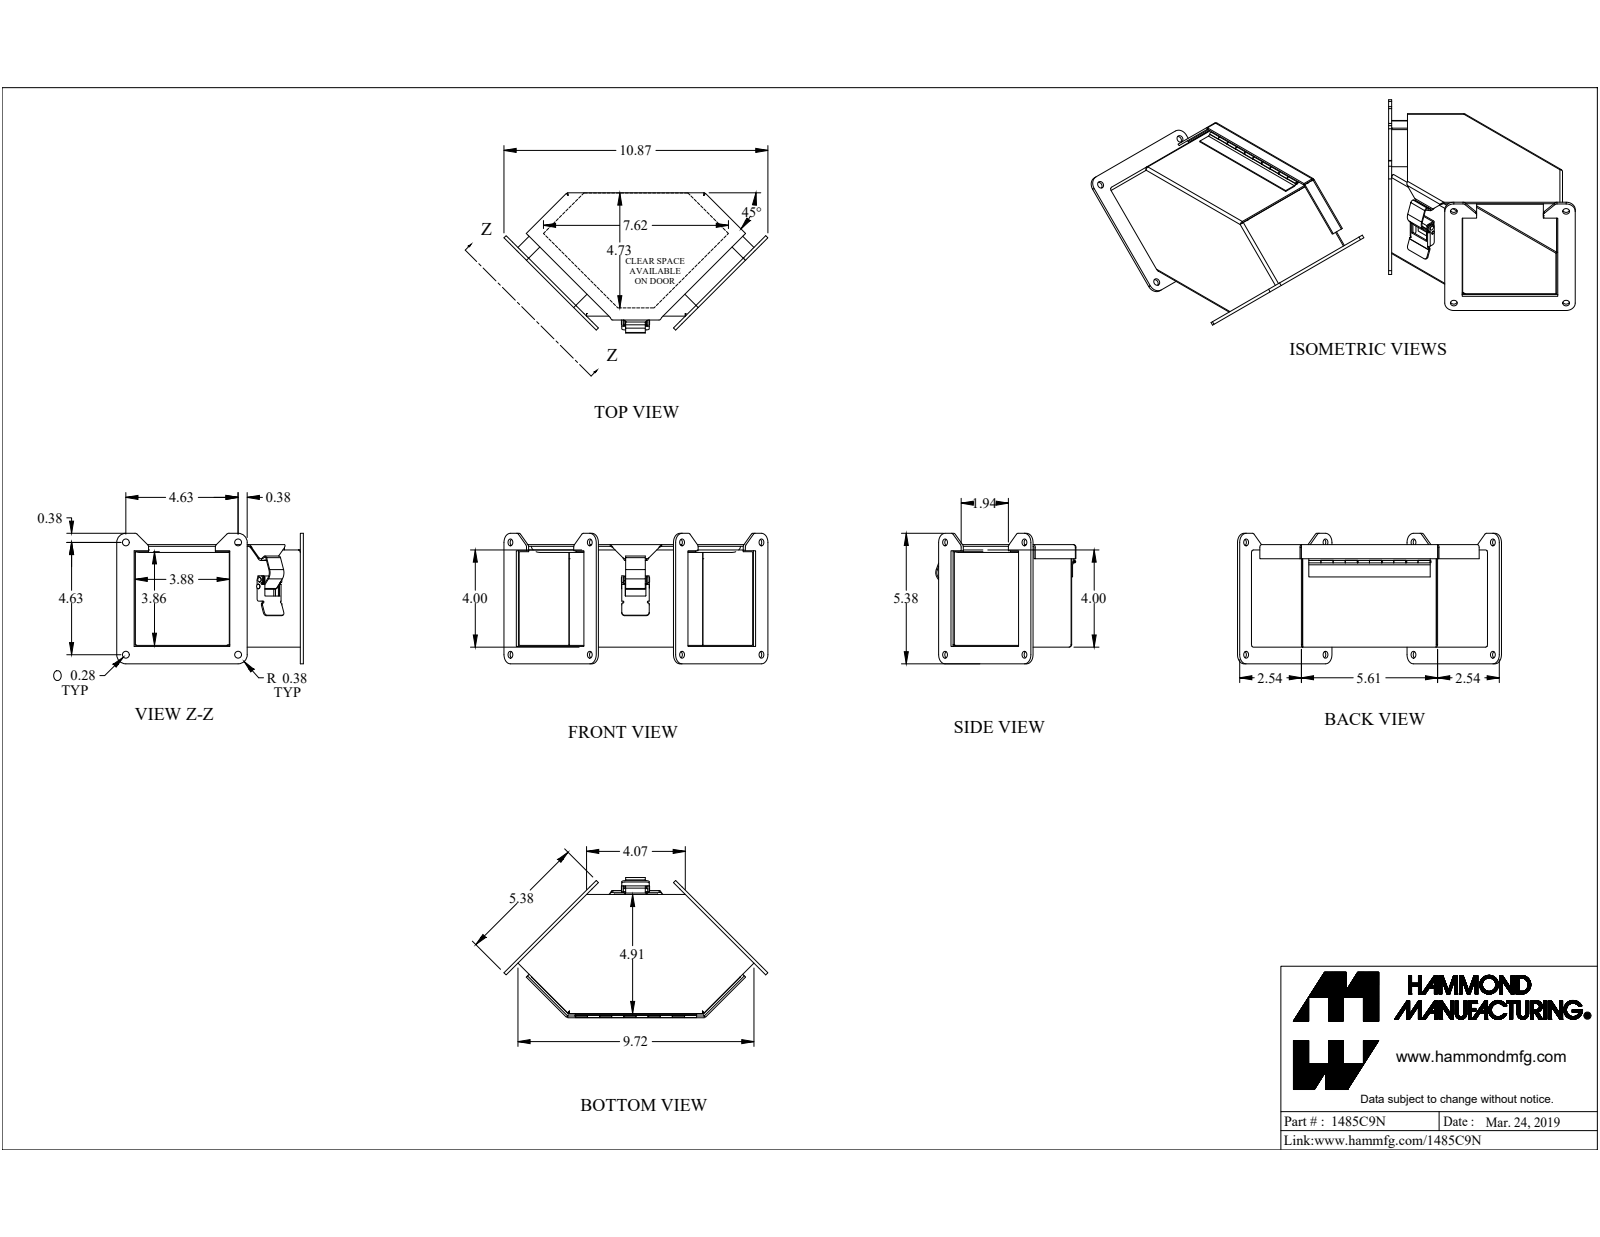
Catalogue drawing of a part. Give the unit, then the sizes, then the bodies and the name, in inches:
Units: inches
Overall size (bounding box): 10.872 × 5.775 × 5.375
Round holes (diameter × count): ⌀0.281 ×8, ⌀0.13 ×1, ⌀0.164 ×1
Round bosses / shafts (diameter × count): ⌀0.187 ×2, ⌀0.156 ×1, ⌀0.125 ×1, ⌀0.1 ×1, ⌀0.045 ×1
Partial cylindrical surfaces — rounded edges, fillets, slot ends (radius × count): R0.036 ×13, R0.108 ×13, R0.125 ×11, R0.375 ×8, R0.016 ×7, R0.25 ×6, R0.035 ×3, R0.039 ×3
Main face-to-face distances: 0.072, 4.15, 4.078, 4.834, 4.222, 6.874, 6.802, 6.999, 6.927, 0.125
Hole centre spacings: 4.625, 6.541, 0.285
Volume: 15.44 in³ · Surface area: 396.5 in²
Bodies: 11 solids, 382 faces (218 planar, 140 cylindrical, 24 other)
Part name (STEP PRODUCT): 1485C9N
STEP written by: SolidWorks 2019 (CONFIG_CONTROL_DESIGN)
